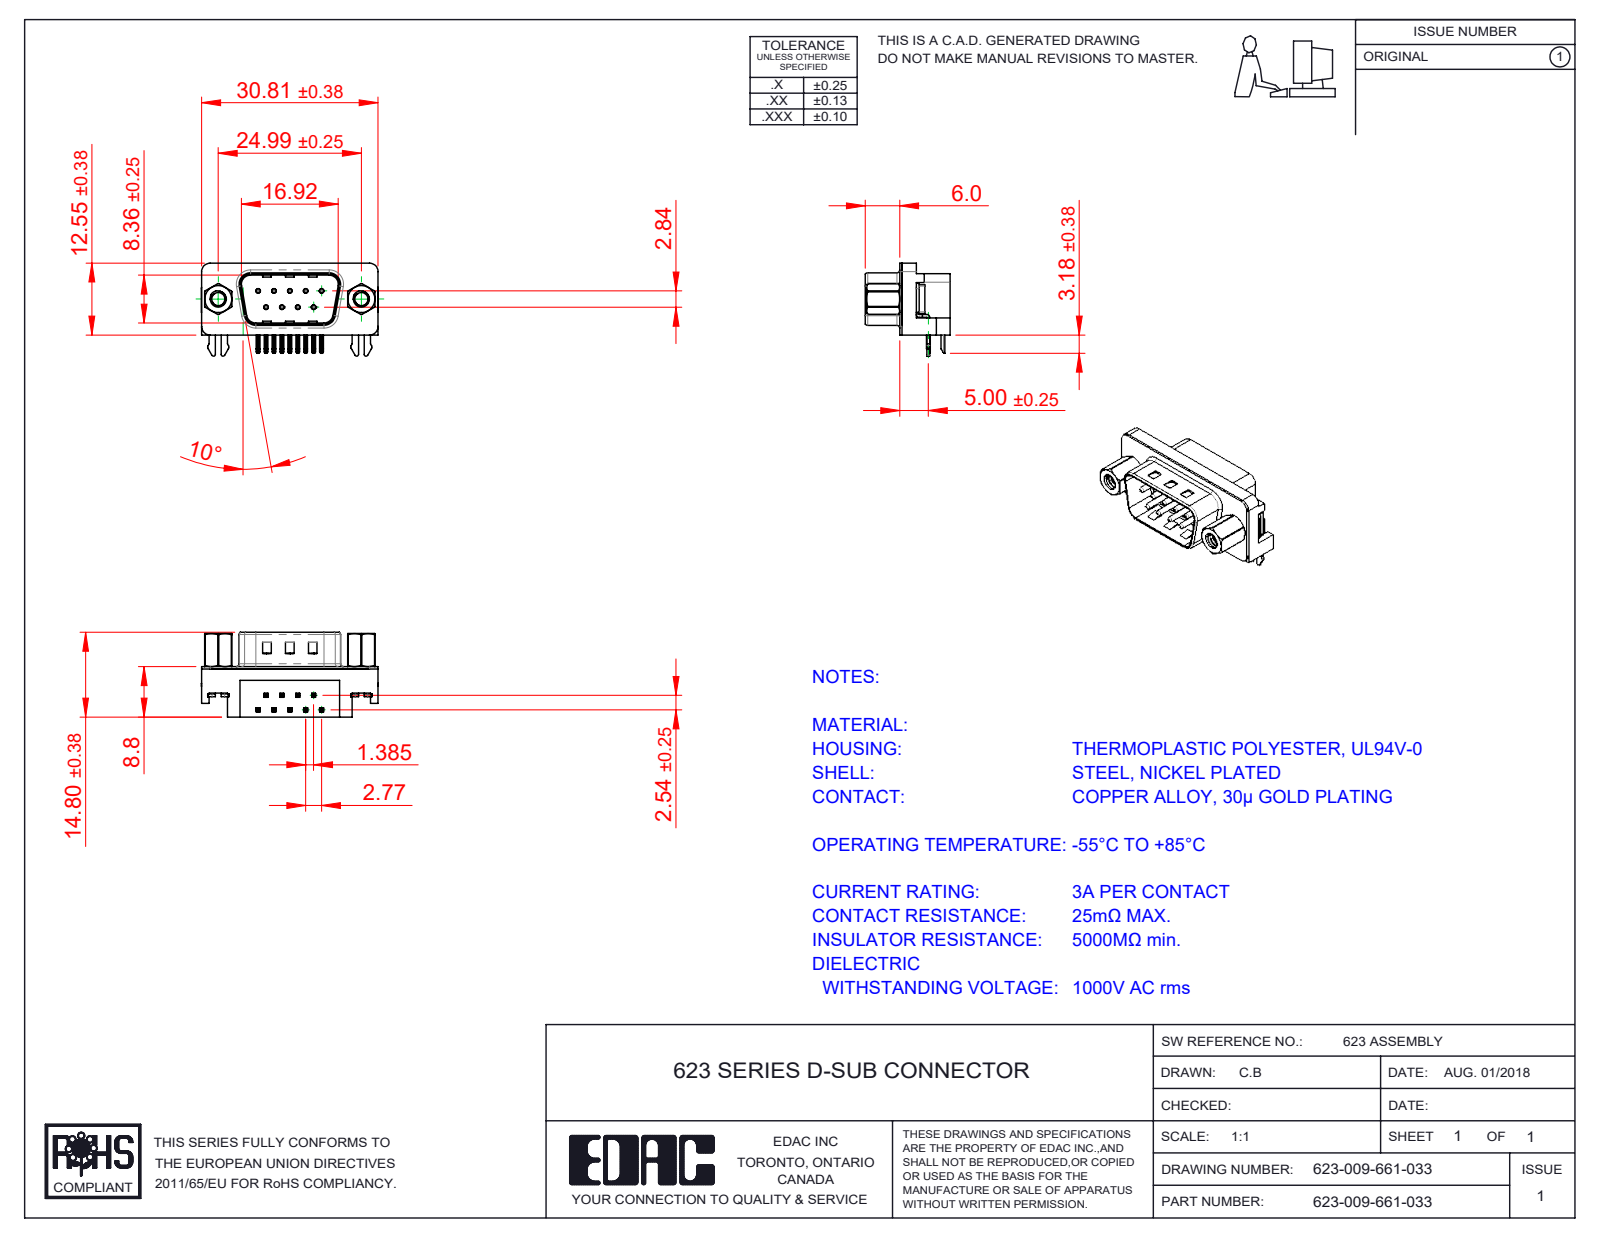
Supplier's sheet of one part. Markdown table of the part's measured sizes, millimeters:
| quantity | value |
| --- | --- |
| part name | 623-009-661-033; 623 Contact Bottom; 623 Housing_9 Socket; 623 4-40 Threaded Rivet (+4 more) |
| STEP written by | SolidWorks 2016 (CONFIG_CONTROL_DESIGN) |
| units | millimeters |
| bodies | 17 solids, 1137 faces (623 planar, 377 cylindrical, 137 other) |
| overall size | 30.89 × 16.25 × 14.8 |
| volume | 2 685 mm³ |
| surface area | 4 308 mm² |
| round holes (diameter × count) | 0.35 × 9, 0.8 × 9, 2.26 × 2, 2.29 × 2, 4 × 2, 4.8 × 2, 5 × 2 |
| round bosses / shafts (diameter × count) | 0.75 × 9, 4.9 × 2, 4.75 × 2, 3.9 × 2, 2.79 × 2 |
| partial cylindrical surfaces (radius × count) | 0.25 × 44, 0.12 × 18, 0.5 × 14, 1 × 8, 1.5 × 8, 0.32 × 4, 0.9 × 4, 1.6 × 4 |
| main face-to-face distances | 0.4, 8.4, 8.8, 5.9, 2.9, 2.5, 0.35, 8.76, 10.69, 10.34 |
| hole center spacings | 3.16, 2.77, 5.54, 5.03, 5.04, 8.31, 7.48, 7.49 |
